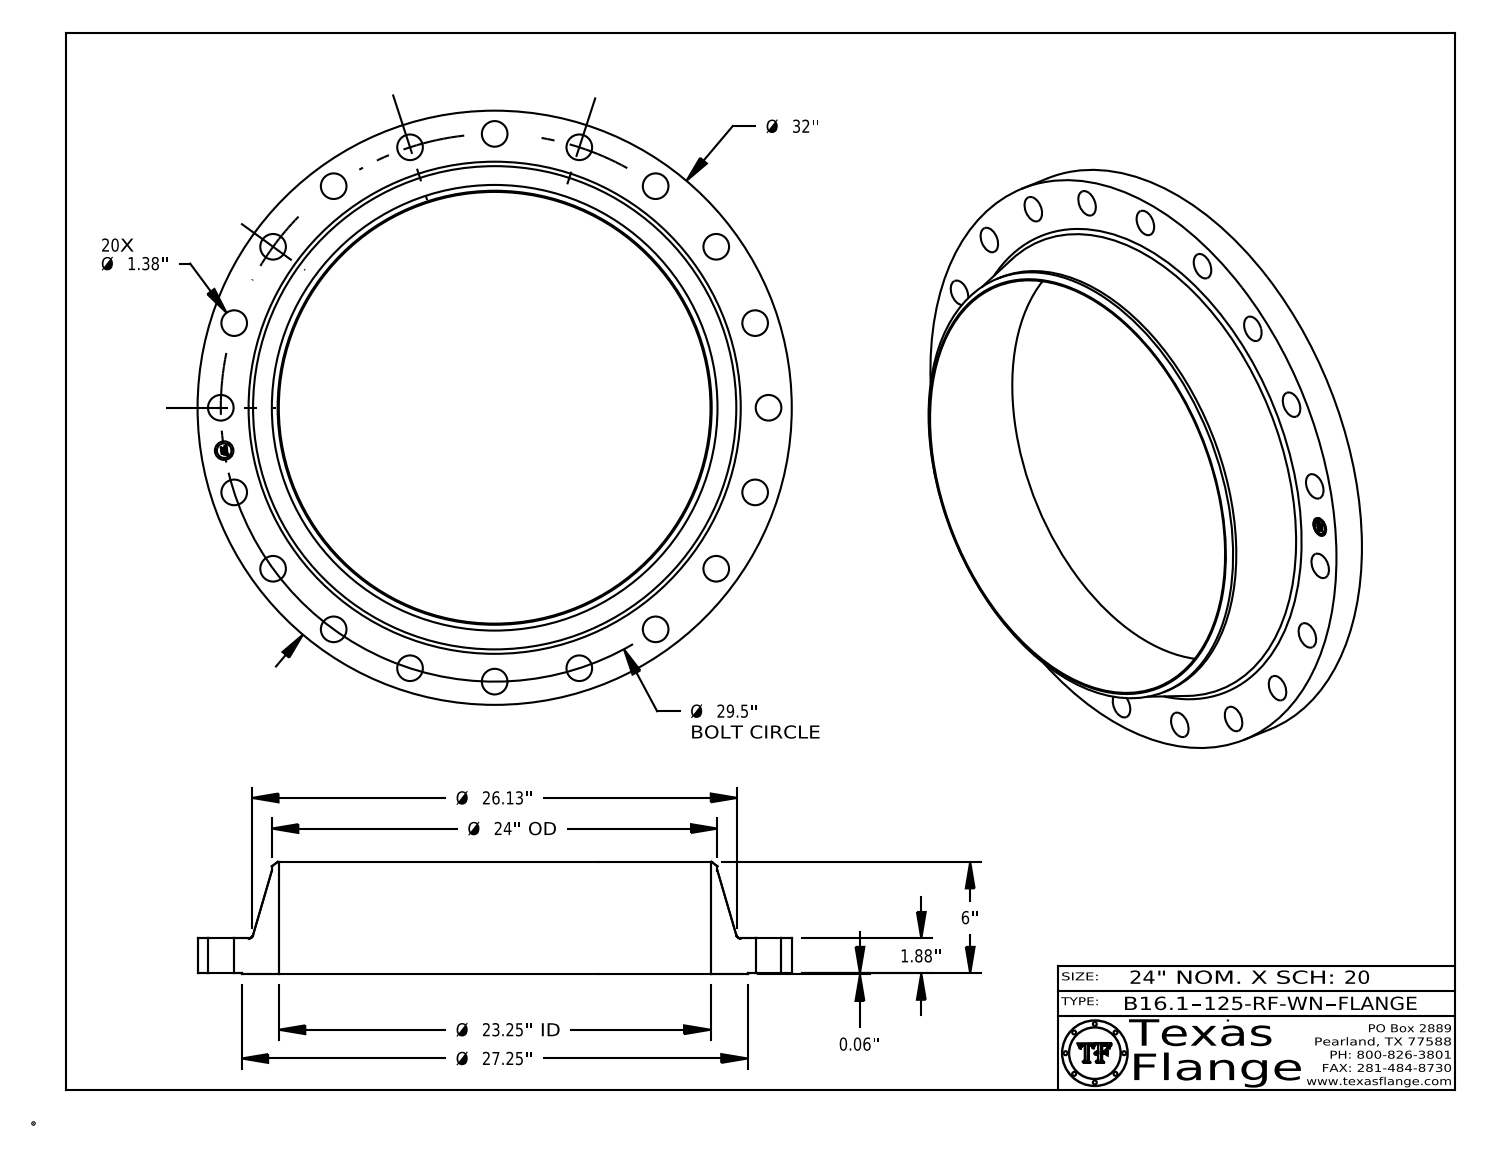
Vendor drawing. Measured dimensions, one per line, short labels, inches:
name: B16.1, Class 125-RF-WN
written by: CATIA V5 STEP AP214 (AUTOMOTIVE_DESIGN)
unit: in
bodies: 1 solid, 443 faces (369 planar, 68 cylindrical, 6 other)
size: 32 × 32 × 6.063
volume: 930.6 in³; area: 1 735 in²
holes: 20× ⌀1.38, 1× ⌀1, 1× ⌀23.25
bosses: 8× ⌀0.061, 1× ⌀32, 1× ⌀27.25, 1× ⌀24, 1× ⌀0.788
face distances: 1.88, 0.063, 1.943, 6.063, 6, 4.12, 1.928, 1.865, 0.015, 4.135
hole spacings: 14.75, 29.137, 4.615, 17.34, 20.859, 23.866, 26.285, 9.116
